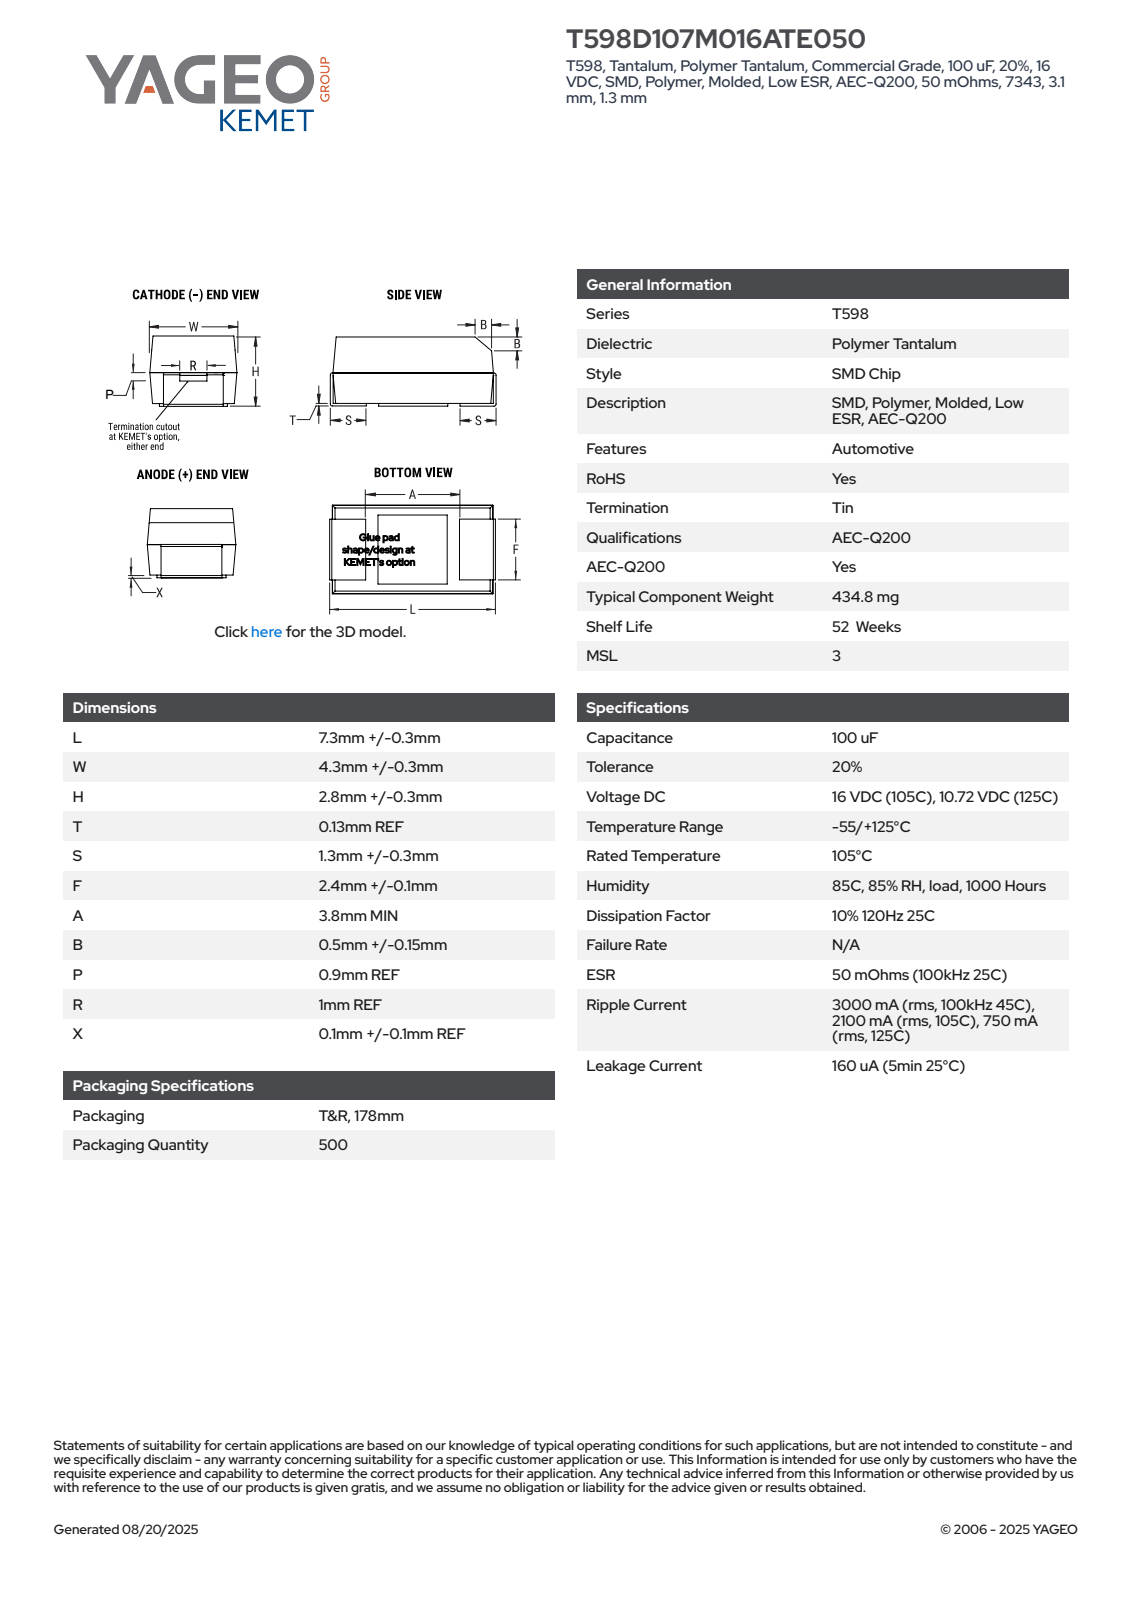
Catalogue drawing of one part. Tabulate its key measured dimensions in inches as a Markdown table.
| quantity | value |
| --- | --- |
| part name | CTSM_TCM2NKKO_7343_L7.6W4.6H3.1T0.13S1.3F2.5A3.8B0.65P0.9R1X0.1 |
| STEP written by | SolidWorks 2021 (AUTOMOTIVE_DESIGN) |
| units | inches |
| bodies | 4 solids, 100 faces (95 planar, 5 cylindrical, 0 other) |
| overall size | 0.299 × 0.181 × 0.123 |
| volume | 0.006 in³ |
| surface area | 0.223 in² |
| partial cylindrical surfaces (radius × count) | 0.004 × 4 |
| main face-to-face distances | 0.118, 0.122, 0.178, 0.179, 0.123, 0.294, 0.299, 0.289, 0.094, 0.205 |
